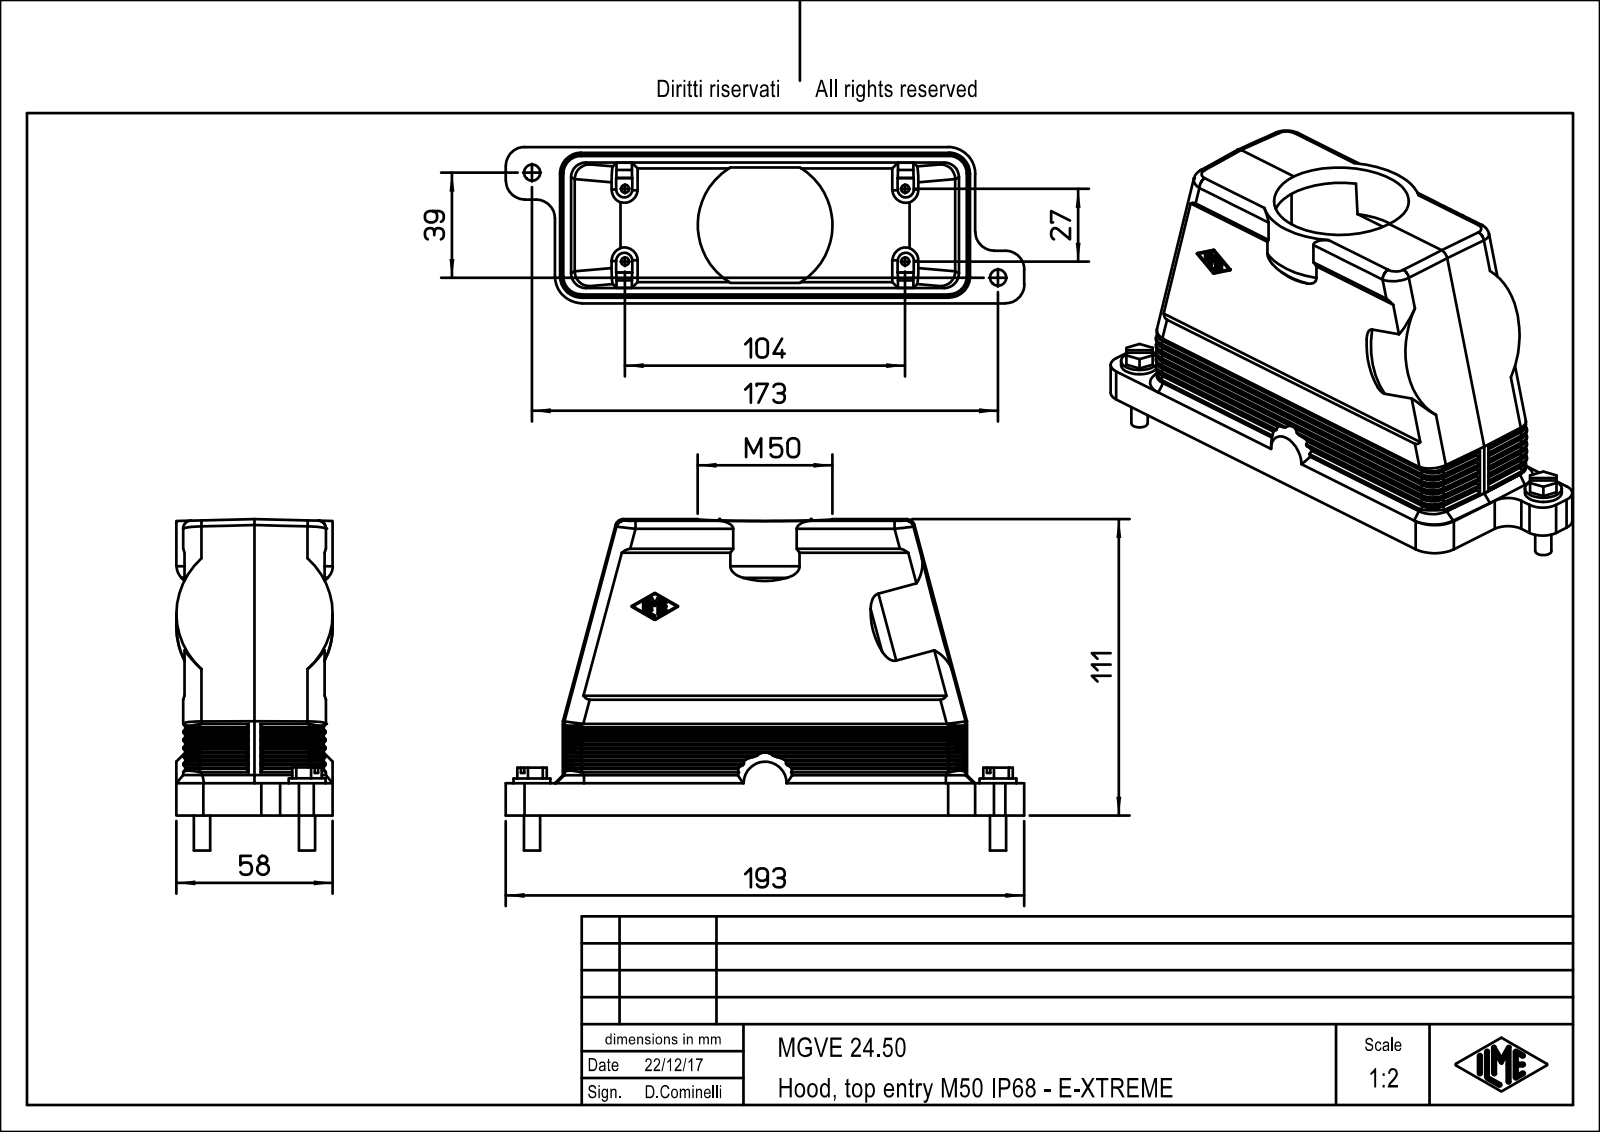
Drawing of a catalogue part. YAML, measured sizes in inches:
part_name: "MGVE_24.50"
step_written_by: "PTC Creo Elements/Direct Modeling 19.0E 27-Jun-2016 (C) Parametric Technology GmbH (AUTOMOTIVE_DESIGN)"
units: inches
bodies: {solids: 1, faces: 536, planar: 257, cylindrical: 123, other: 156}
overall_size: [7.579, 4.843, 2.283]
volume: 12.68
surface_area: 151.5
round_holes:
  - {diameter: 0.118, count: 4}
  - {diameter: 1.969, count: 1}
round_bosses_or_shafts:
  - {diameter: 0.539, count: 2}
  - {diameter: 0.236, count: 2}
partial_cylinders:
  - {radius: 0.276, count: 62}
  - {radius: 0.013, count: 15}
  - {radius: 0.217, count: 8}
  - {radius: 0.287, count: 4}
  - {radius: 0.007, count: 2}
  - {radius: 0.394, count: 2}
  - {radius: 1.142, count: 2}
  - {radius: 0.007, count: 1}
face_to_face_distances: [2.047, 0.118, 2.165, 0.02, 0.098, 2.185, 2.067, 0.131, 4.114, 2.283]
hole_center_spacings: [2.115, 1.063, 4.094, 4.23]
